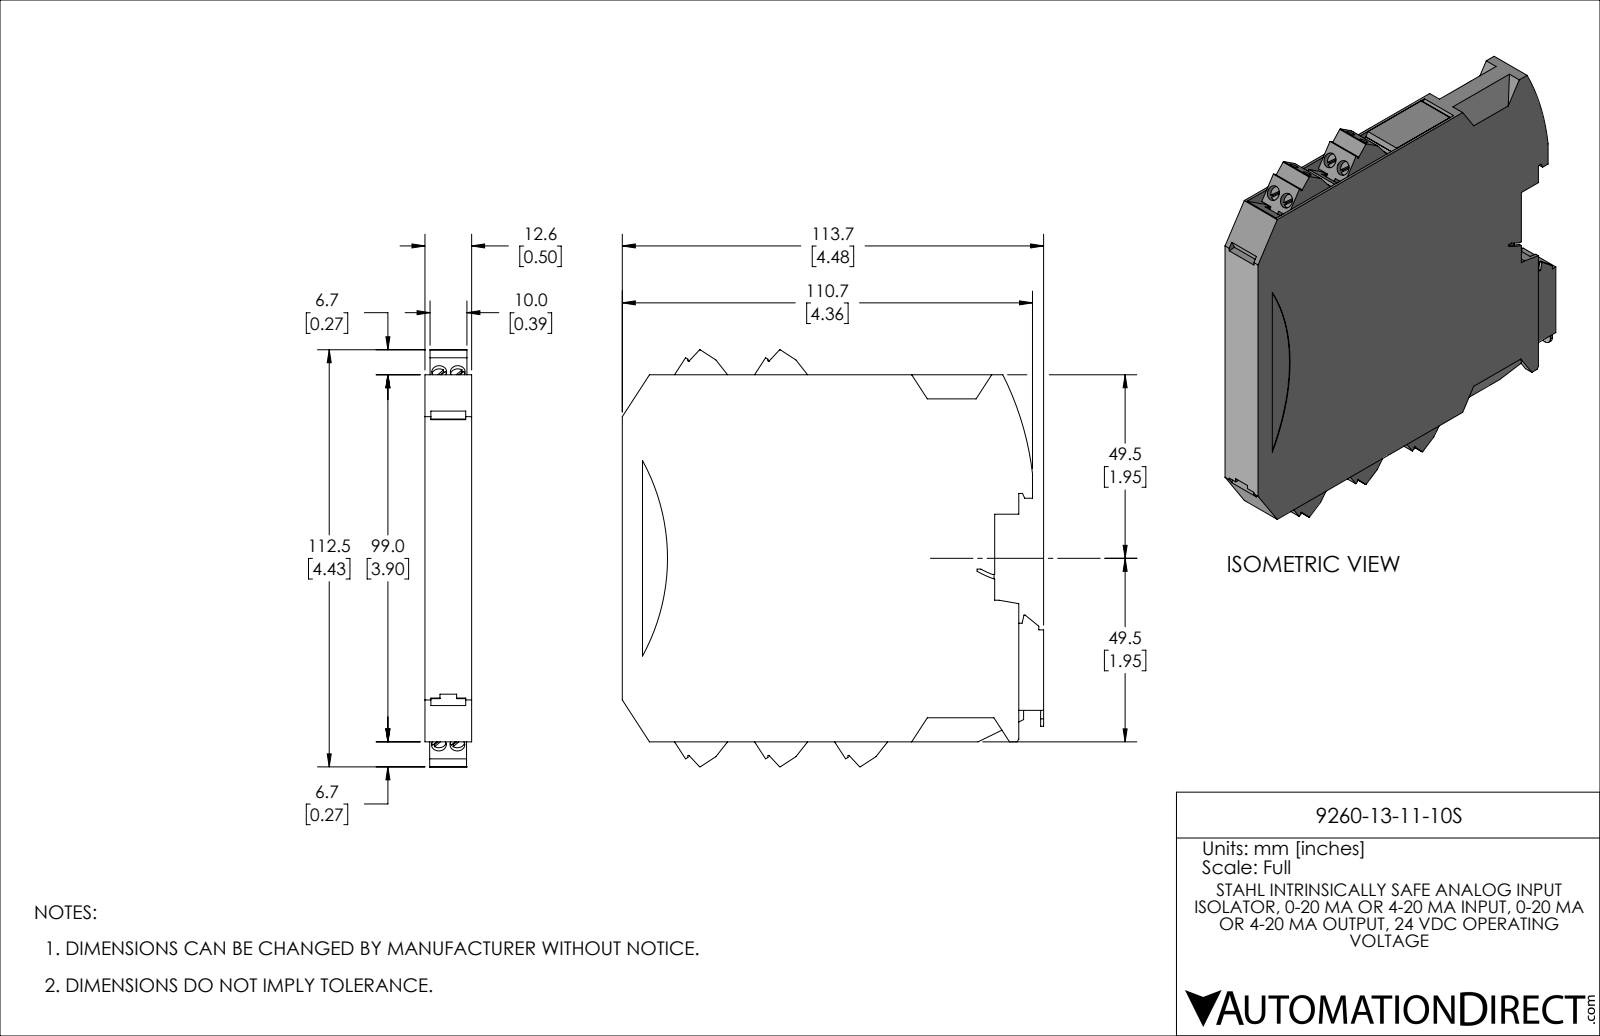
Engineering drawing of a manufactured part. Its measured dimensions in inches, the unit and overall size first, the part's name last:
Units: inches
Overall size (bounding box): 4.476 × 4.429 × 0.496
Round holes (diameter × count): ⌀0.06 ×10, ⌀0.088 ×10, ⌀0.118 ×10, ⌀0.157 ×10
Round bosses / shafts (diameter × count): ⌀0.11 ×6
Partial cylindrical surfaces — rounded edges, fillets, slot ends (radius × count): R0.118 ×13, R0.114 ×10, R0.055 ×6, R0.008 ×5, R0.079 ×2, R0.02 ×1, R0.059 ×1, R0.098 ×1
Main face-to-face distances: 0.496, 0.03, 0.467, 0.713, 0.392, 0.05, 0.446, 0.021, 0.416, 0.054
Hole centre spacings: 0.197, 0.713, 0.74, 0.849, 0.872, 0.463, 0.503, 0.463
Volume: 7.755 in³ · Surface area: 64.57 in²
Bodies: 7 solids, 956 faces (854 planar, 92 cylindrical, 10 other)
Part name (STEP PRODUCT): 9260-13-11-10s
STEP written by: SolidWorks 2019 (AUTOMOTIVE_DESIGN)
